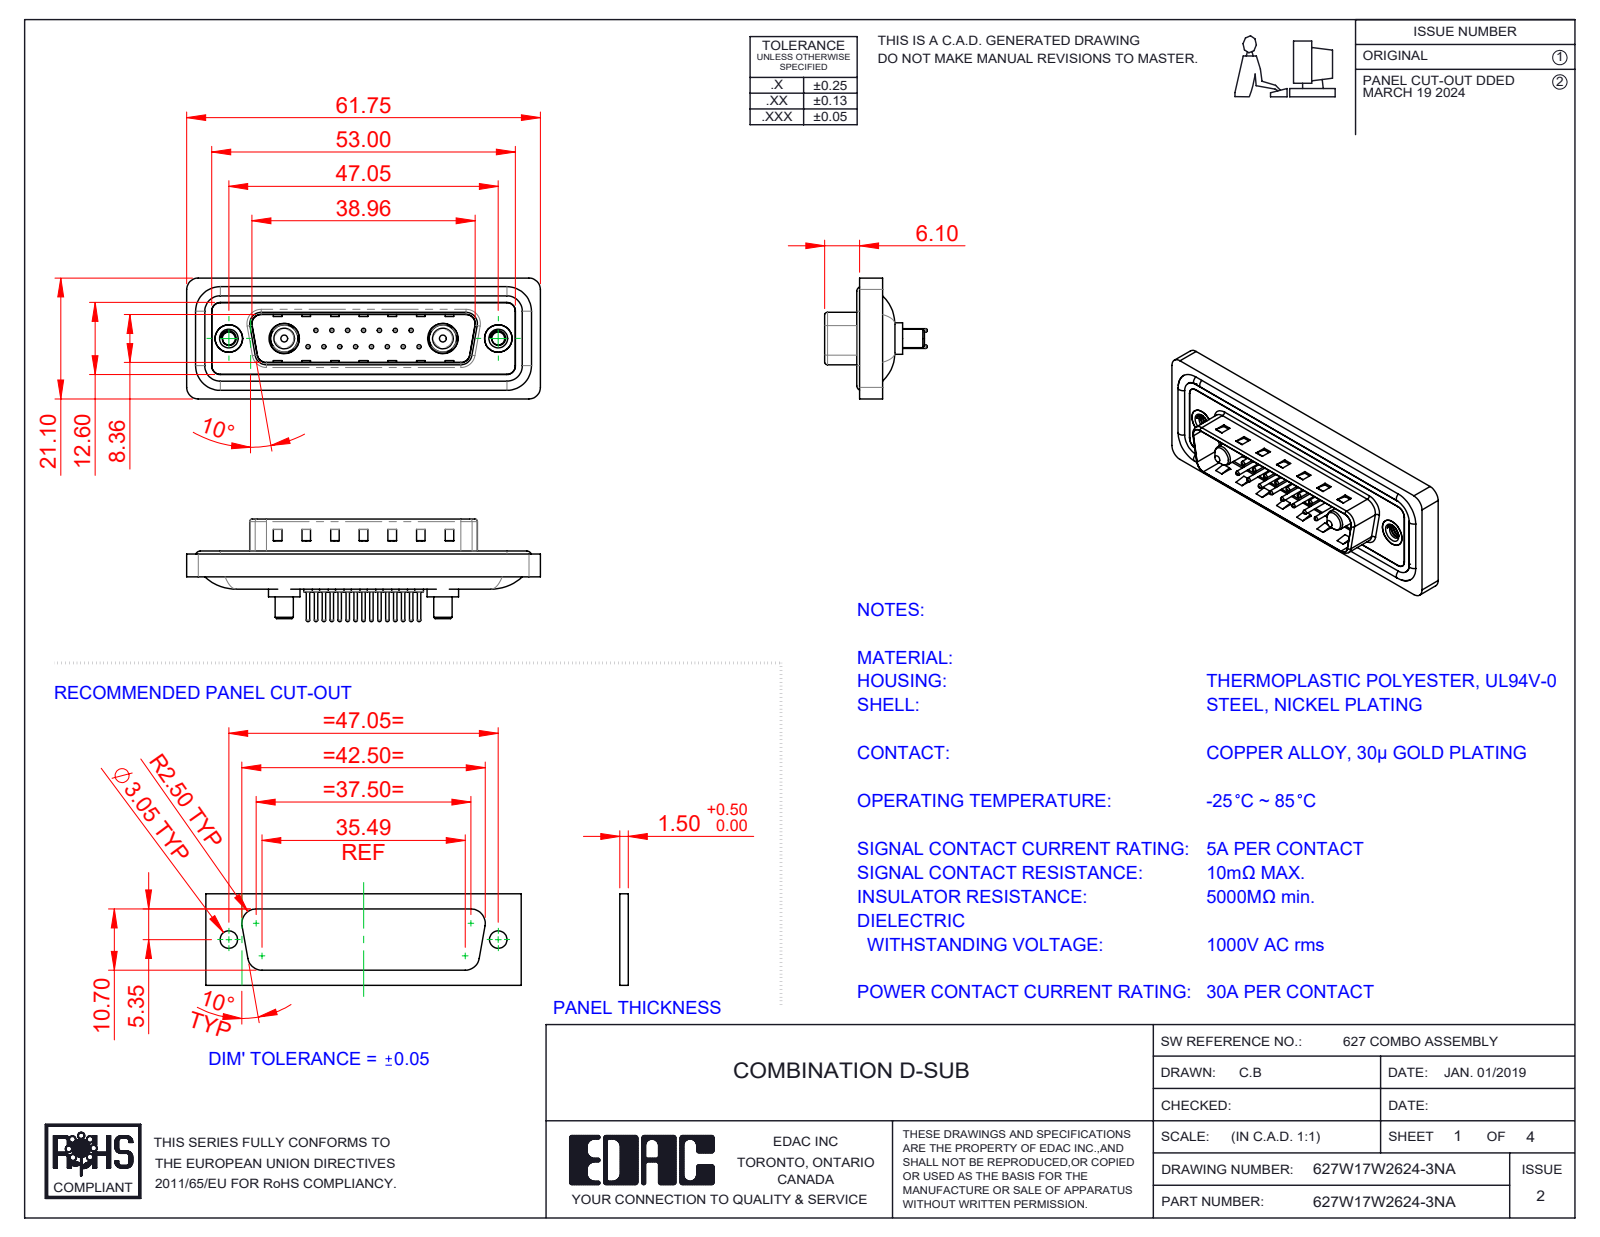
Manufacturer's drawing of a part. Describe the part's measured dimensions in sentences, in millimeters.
The part is named "627Combo Housing_17W2; 627W17W2624-3NA; 627Combo Threaded Rivet_A; 627Combo Contact Row 1_24 (+5 more)". Its 3-D file was written by "SolidWorks 2023 (CONFIG_CONTROL_DESIGN)". It is 26 solids with 1114 faces: 334 planar, 438 cylindrical and 342 other. Overall it measures 61.75 by 21.1 by 17.9 millimeters. Its volume is 7 282 cubic millimeters and its surface area 11 921 square millimeters. Round holes: 15 of diameter 0.75, 15 of diameter 1.6, 15 of diameter 2, 2 of diameter 2.26, 2 of diameter 4, 2 of diameter 4.8, 2 of diameter 4.85, 2 of diameter 5, 2 of diameter 5.3. Round bosses or shafts: 15 of diameter 1.5, 15 of diameter 0.6, 4 of diameter 1.6, 2 of diameter 5.5, 2 of diameter 5.2, 2 of diameter 4.9, 2 of diameter 4.75, 2 of diameter 3.75. Partial cylindrical surfaces (rounded edges, fillets, slot ends): 22 of radius 1.5, 18 of radius 2, 8 of radius 0.5, 8 of radius 1.6, 4 of radius 0.25, 4 of radius 0.6, 4 of radius 0.65, 4 of radius 0.9. The main face-to-face distances are 0.4, 1.5, 1.1, 1.6, 0.5, 3.1, 2.9, 0.82, 9.58, 4.1. The hole center spacings are 3.16, 2.77, 5.54, 8.31, 5.04, 7.49, 11.08, 5.03.
